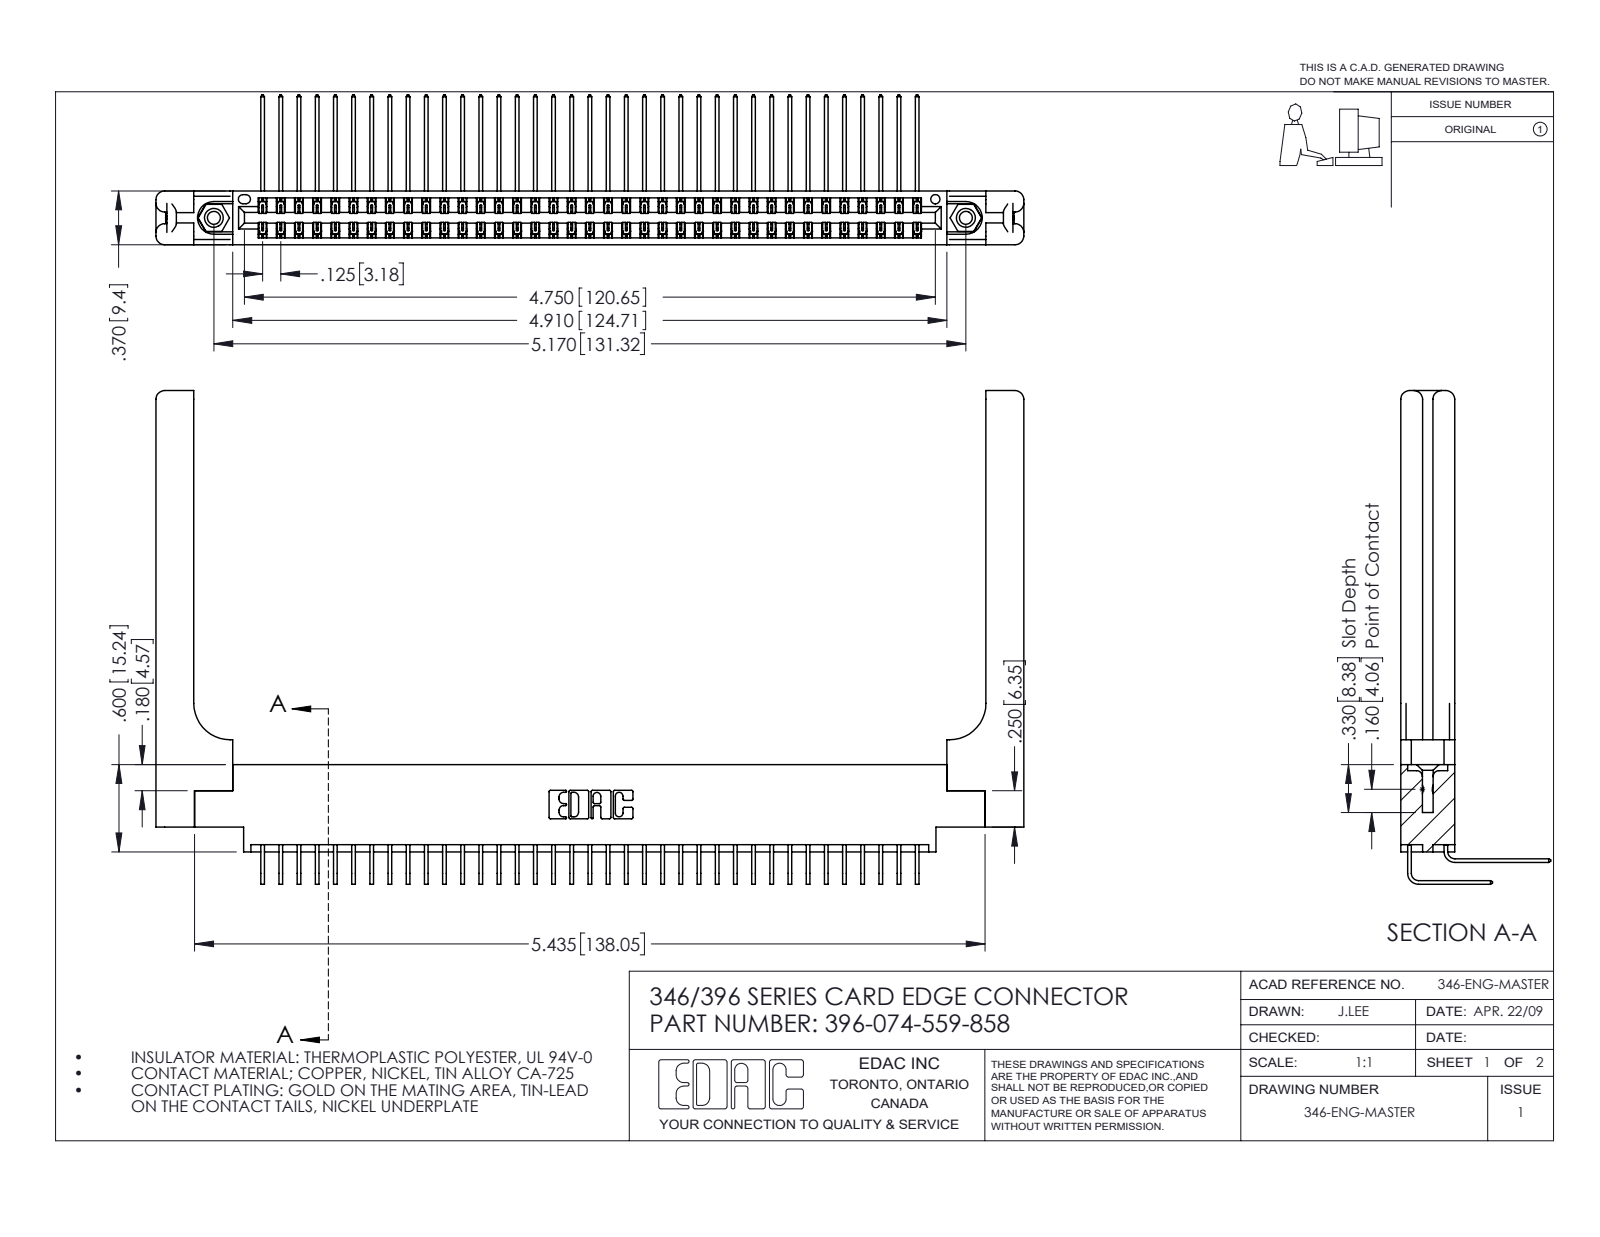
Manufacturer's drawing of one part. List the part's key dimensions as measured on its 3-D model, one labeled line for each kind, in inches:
Part name (STEP PRODUCT): 345-292-001_558 559 Tail - 1; 346-220-058_345-220-058; 346 Part_0.170 Offset - 0.156 Dia-TH; 396-074-559-858 (+2 more)
STEP written by: SolidWorks 2016 (CONFIG_CONTROL_DESIGN)
Units: inches
Bodies: 79 solids, 4378 faces (2966 planar, 1352 cylindrical, 60 other)
Overall size (bounding box): 5.966 × 3.393 × 1.03
Volume: 1.373 in³ · Surface area: 43.02 in²
Round holes (diameter × count): ⌀0.089 ×2, ⌀0.125 ×2, ⌀0.156 ×2, ⌀0.064 ×1
Round bosses / shafts (diameter × count): ⌀0.155 ×2
Partial cylindrical surfaces — rounded edges, fillets, slot ends (radius × count): R0.006 ×111, R0.01 ×22, R0.06 ×16, R0.007 ×6, R0.031 ×6, R0.026 ×3, R0.014 ×2, R0.022 ×2
Main face-to-face distances: 0.37, 0.048, 0.322, 0.072, 0.025, 0.148, 0.15, 0.25, 0.298, 0.275
Hole centre spacings: 0.246, 4.961, 5.17
